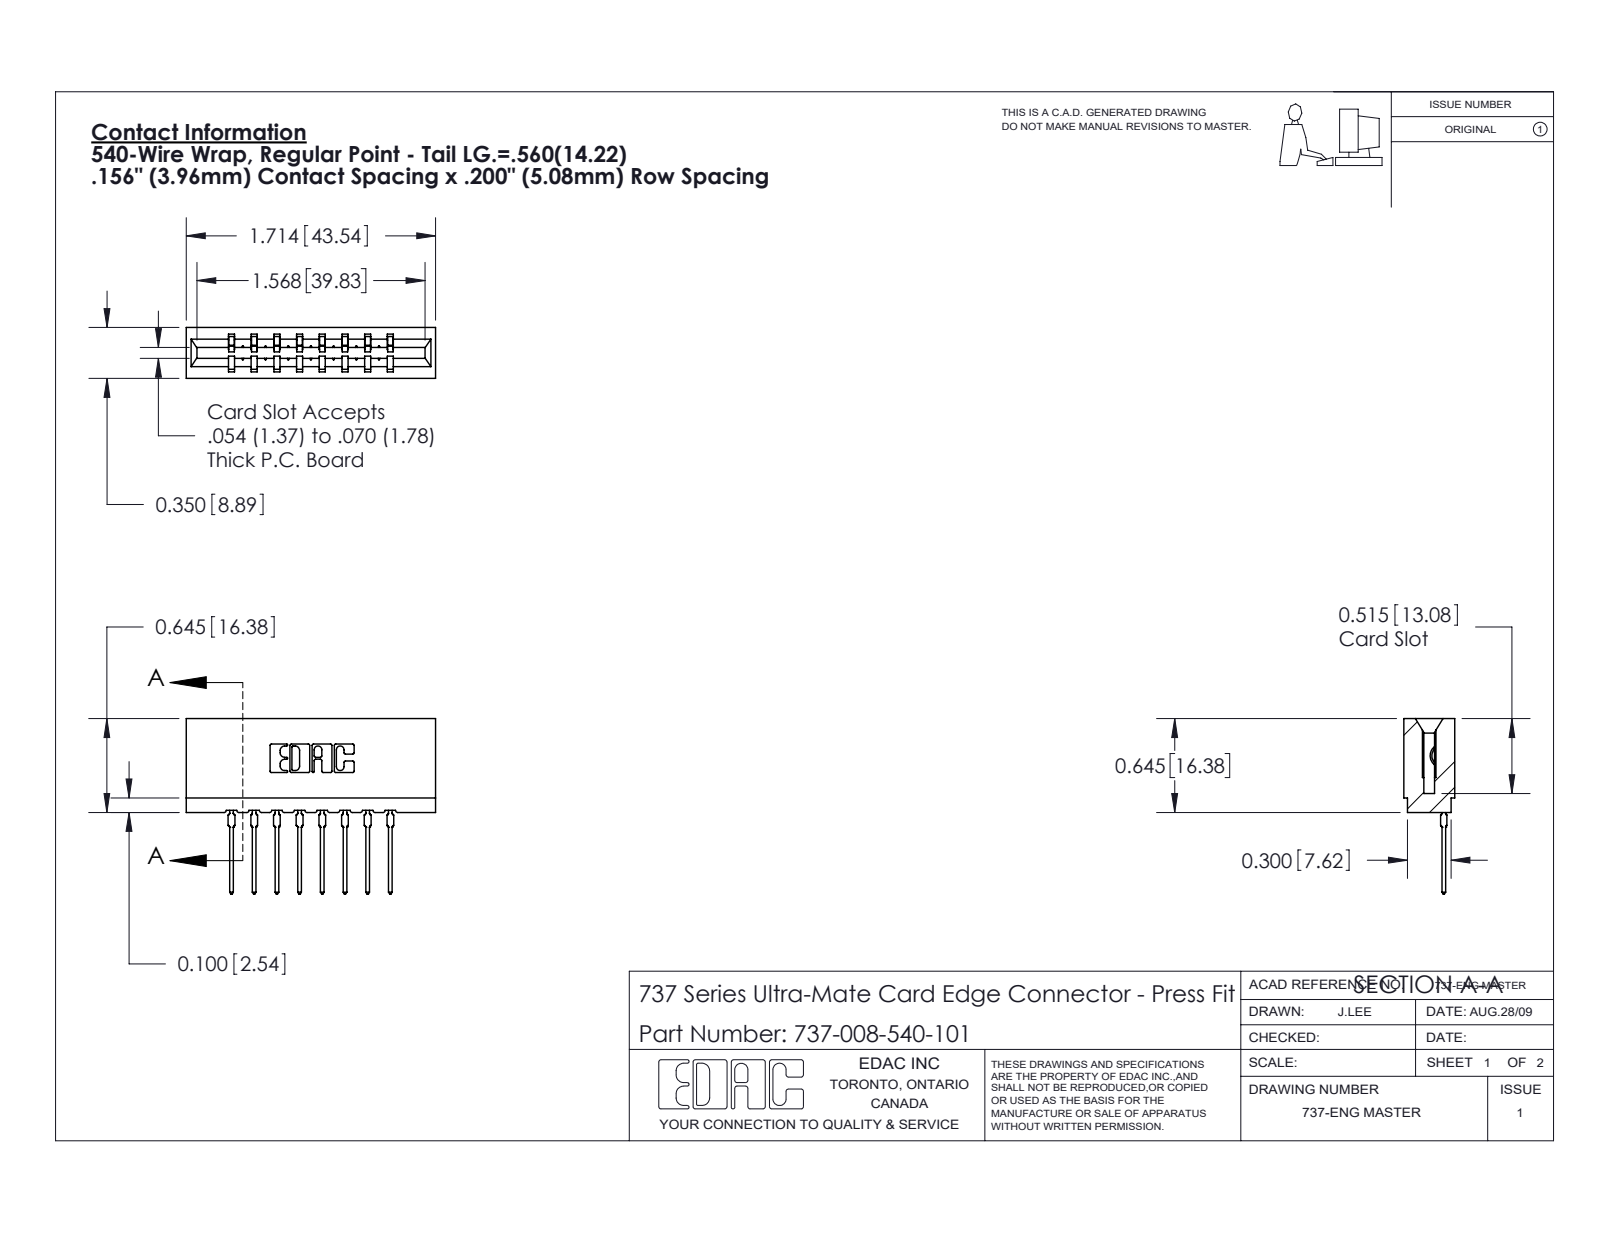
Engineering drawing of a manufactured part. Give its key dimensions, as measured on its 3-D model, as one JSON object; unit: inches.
{"part_name": "745-292-001_540; 737 Part_Insulator Option - 01; 737-008-540-101", "step_written_by": "SolidWorks 2020 (CONFIG_CONTROL_DESIGN)", "units": "inches", "bodies": {"solids": 9, "faces": 998, "planar": 598, "cylindrical": 192, "other": 208}, "overall_size": [1.714, 1.206, 0.35], "volume_in3": 0.272, "surface_area_in2": 8.469, "partial_cylinders_radius": [[0.01, 22], [0.015, 16], [0.021, 16], [0.007, 6], [0.031, 6], [0.005, 4], [0.011, 4], [0.026, 3]], "face_to_face_distances": [0.156, 0.138, 0.212, 0.35, 0.624, 0.312, 0.354, 0.198, 0.468, 0.78]}
